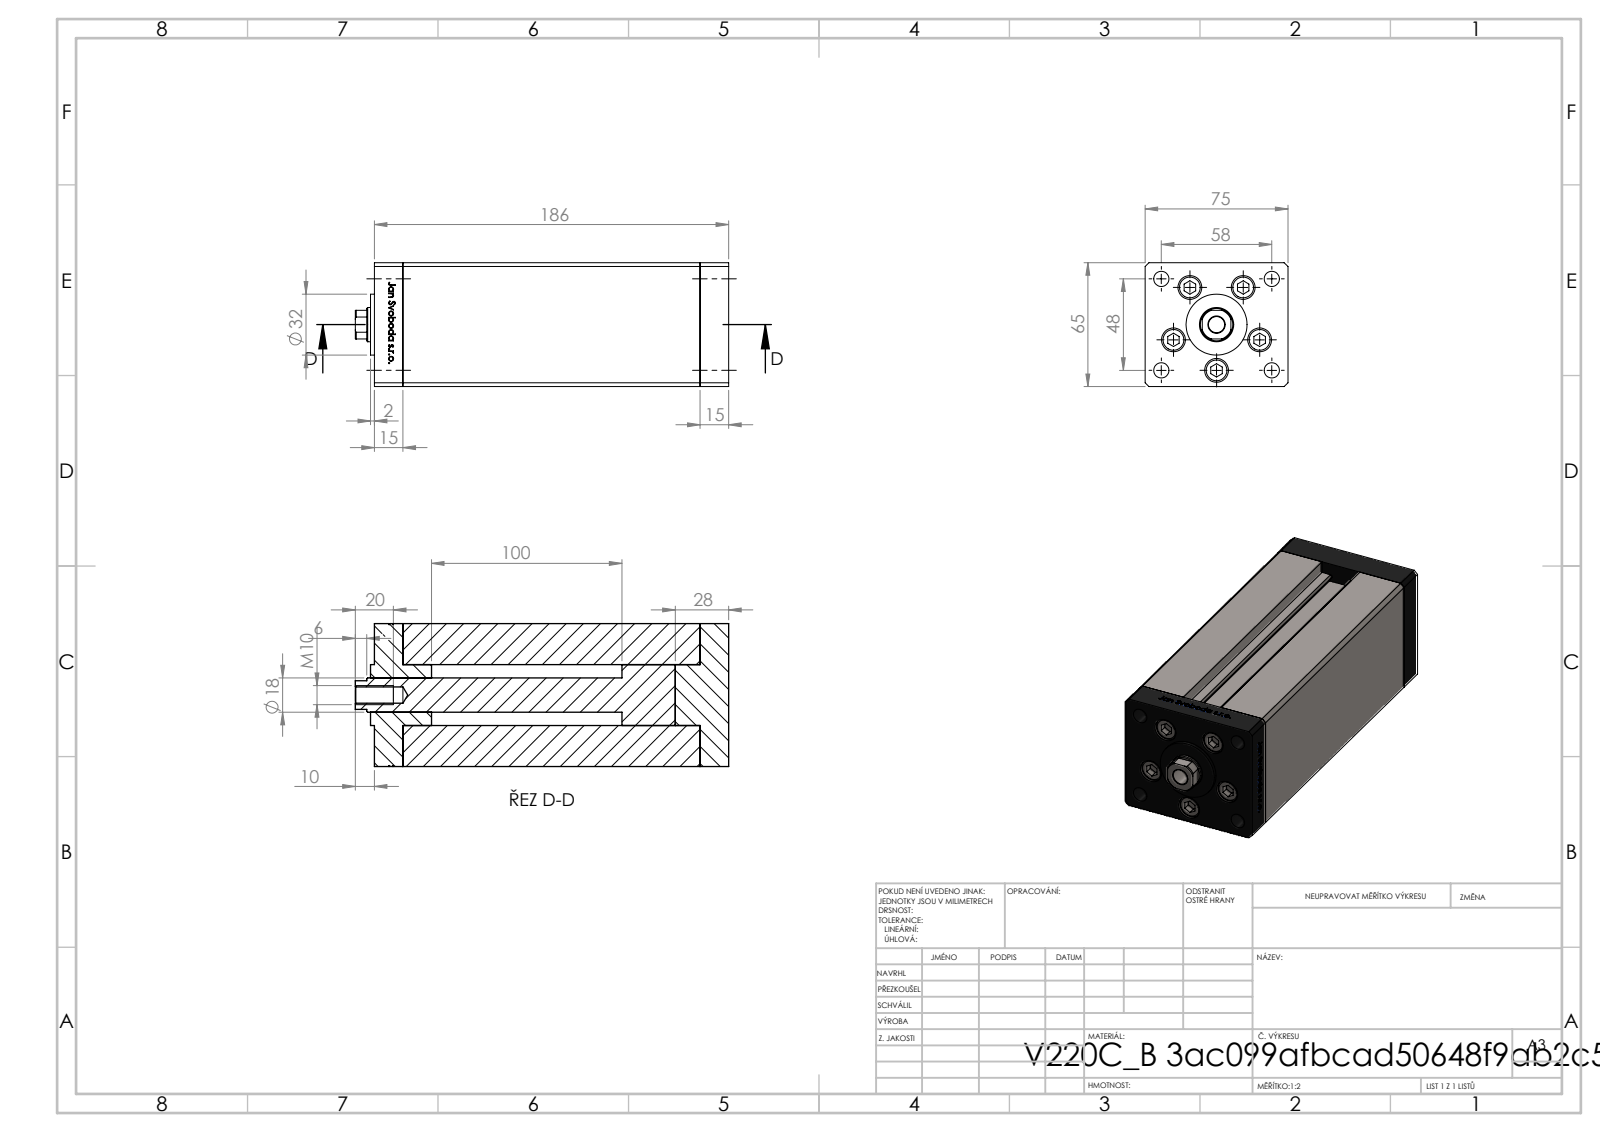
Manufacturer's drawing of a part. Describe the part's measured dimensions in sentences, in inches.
The part is named "V220C_VC_B; V220C_B MIDDLE; ALLEN BOLT; V220C BACK_B (+1 more)". Its 3-D file was written by "SolidWorks 2019 (CONFIG_CONTROL_DESIGN)". It is 14 solids with 1183 faces: 462 planar, 147 cylindrical and 574 other. Overall it measures 7.717 by 2.953 by 2.559 inches. Its volume is 49.12 cubic inches and its surface area 211.6 square inches. Round holes: 5 of diameter 0.354, 5 of diameter 0.492, 4 of diameter 0.315, 2 of diameter 0.079, 2 of diameter 0.518, 1 of diameter 0.335, 1 of diameter 0.709. Round bosses or shafts: 5 of diameter 0.315, 1 of diameter 1.26. Partial cylindrical surfaces (rounded edges, fillets, slot ends): 2 of radius 0.037, 1 of radius 0.335. The main face-to-face distances are 2.953, 2.559, 0.591, 6.142, 6.732, 7.323, 1.102, 2.146, 0.413, 1.033. The hole center spacings are 0.945, 1.482, 0.617, 0.678, 1.091, 1.135, 1.142, 1.285.
